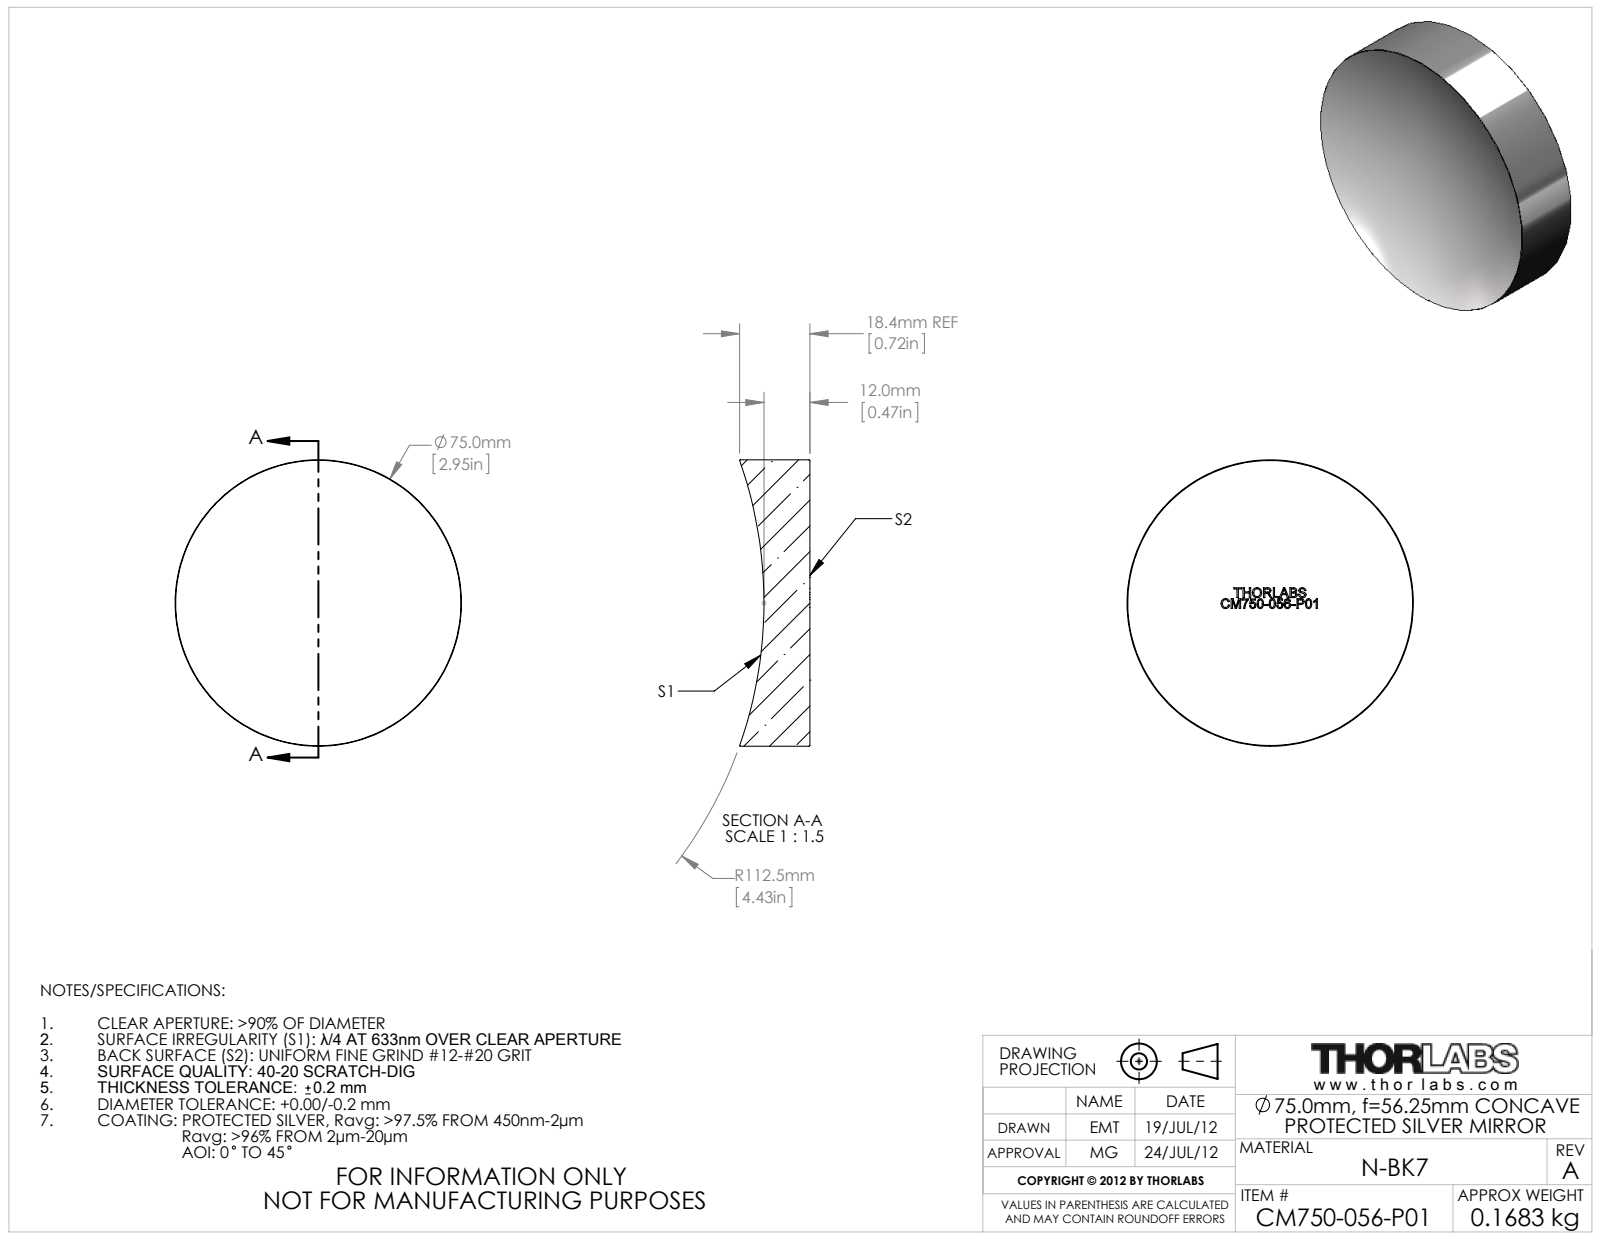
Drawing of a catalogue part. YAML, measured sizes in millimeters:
part_name: "24640-E0W"
step_written_by: "SolidWorks 2011 (CONFIG_CONTROL_DESIGN)"
units: millimeters
bodies: {solids: 0, faces: 40, planar: 32, cylindrical: 2, other: 6}
overall_size: [75, 75, 18.4]
round_bosses_or_shafts:
  - {diameter: 75, count: 1}
